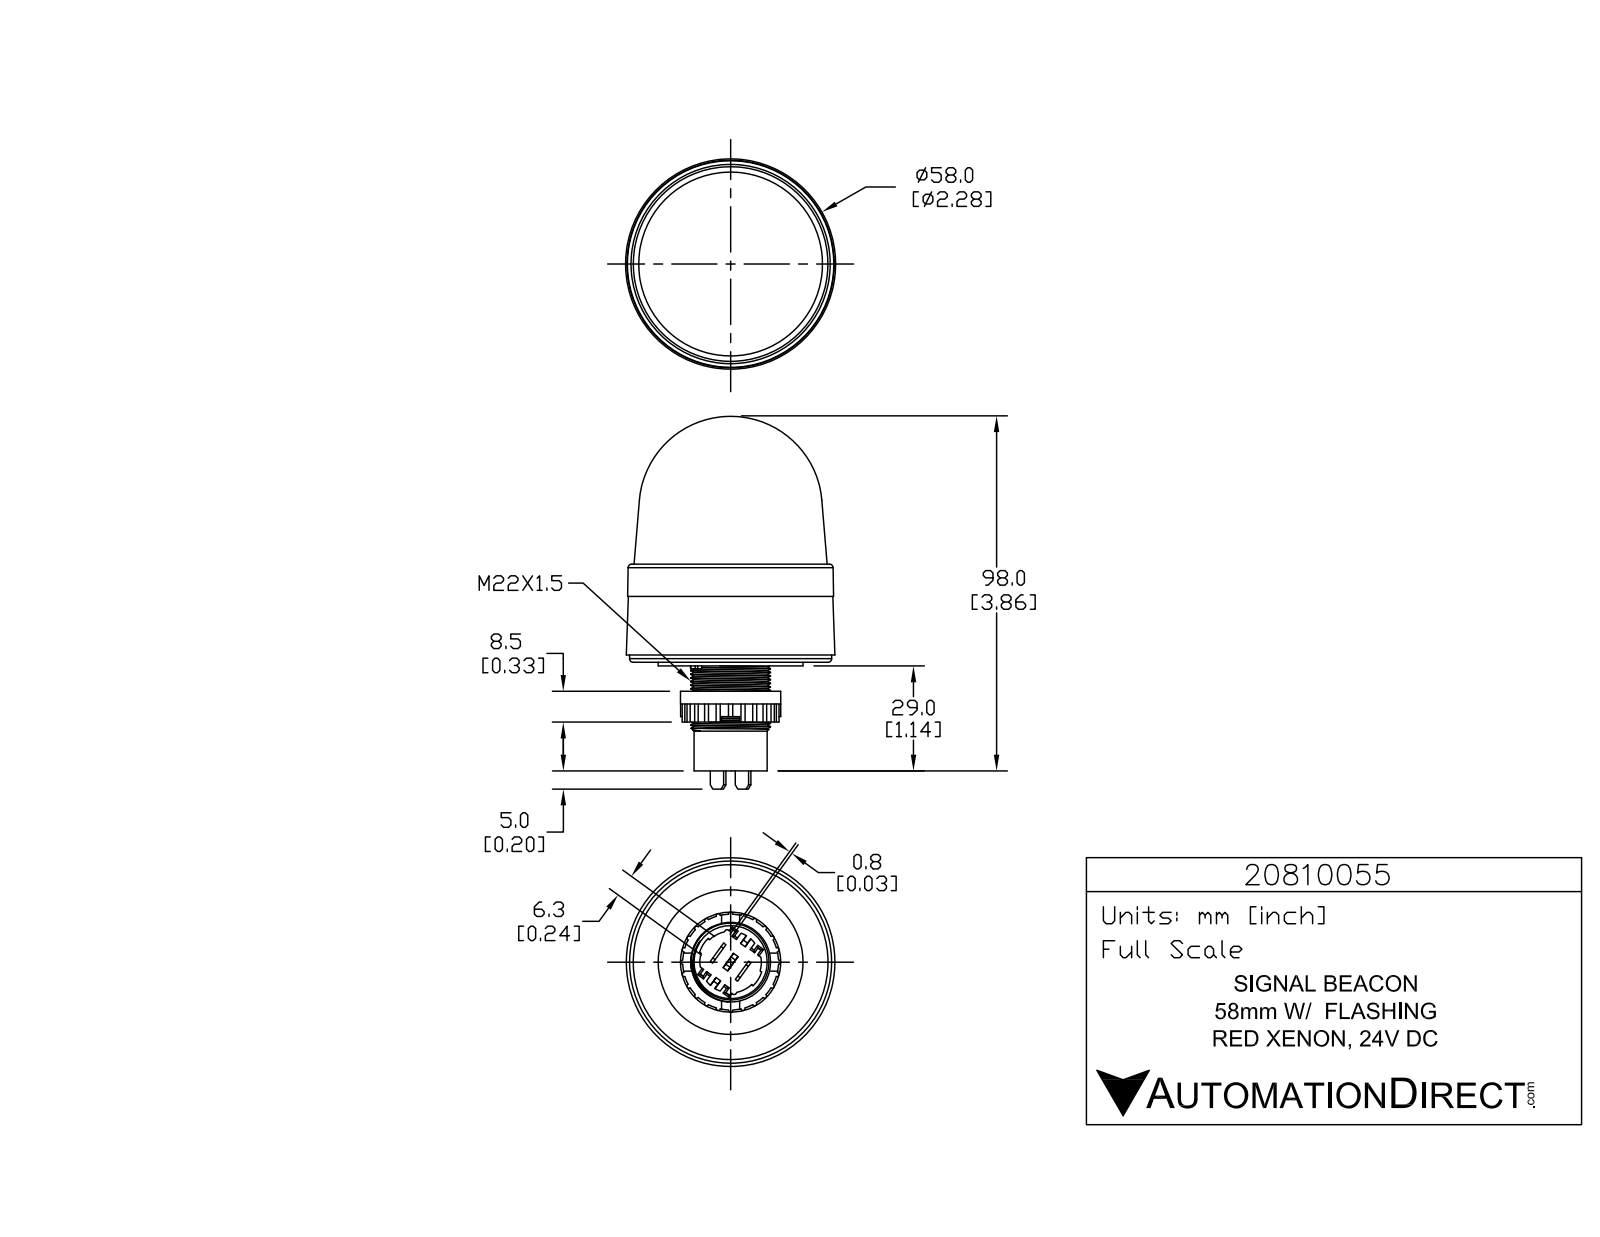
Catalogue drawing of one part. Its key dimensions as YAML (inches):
part_name: "20810055"
step_written_by: "SolidWorks 2015 (AUTOMOTIVE_DESIGN)"
units: inches
bodies: {solids: 1, faces: 266, planar: 119, cylindrical: 120, other: 27}
overall_size: [4.051, 2.269, 2.269]
volume: 9.016
surface_area: 31.05
round_holes:
  - {diameter: 0.906, count: 1}
round_bosses_or_shafts:
  - {diameter: 2.197, count: 1}
  - {diameter: 1.575, count: 1}
  - {diameter: 1.091, count: 1}
  - {diameter: 0.866, count: 1}
  - {diameter: 0.795, count: 1}
partial_cylinders:
  - {radius: 0.023, count: 24}
  - {radius: 0.02, count: 2}
  - {radius: 0.335, count: 1}
  - {radius: 0.354, count: 1}
  - {radius: 0.522, count: 1}
face_to_face_distances: [0.039, 0.276, 0.118, 1.142, 0.335, 0.315, 1.063, 0.748, 1.024, 0.728]
